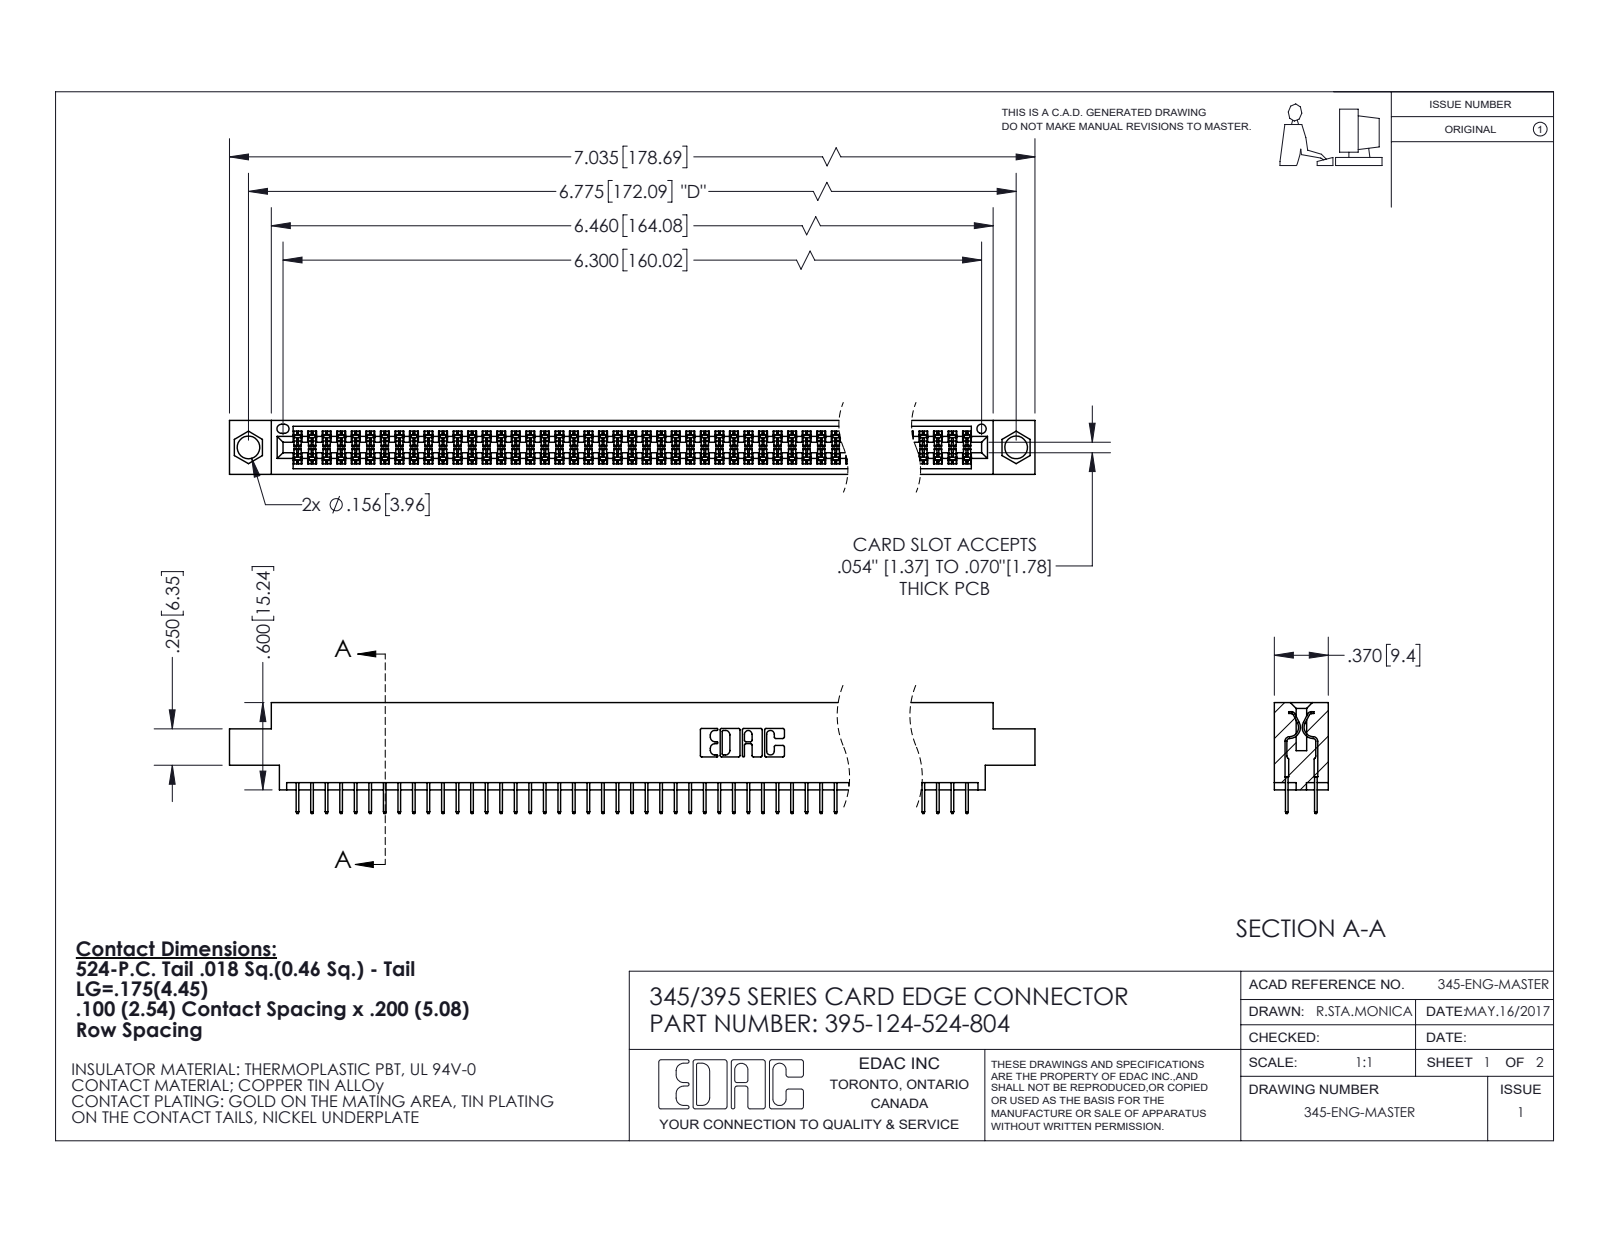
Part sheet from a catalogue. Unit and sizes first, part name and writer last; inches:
Units: inches
Overall size (bounding box): 7.035 × 0.762 × 0.37
Round holes (diameter × count): ⌀0.156 ×2, ⌀0.064 ×1
Partial cylindrical surfaces — rounded edges, fillets, slot ends (radius × count): R0.006 ×247, R0.01 ×22, R0.007 ×6, R0.031 ×6, R0.026 ×3, R0.014 ×2, R0.019 ×2, R0.022 ×2
Main face-to-face distances: 0.072, 0.298, 0.37, 0.2, 0.098, 0.272, 0.025, 0.225, 0.072, 0.175
Hole centre spacings: 0.27, 6.539, 6.775
Volume: 1.046 in³ · Surface area: 39.09 in²
Bodies: 125 solids, 6840 faces (4934 planar, 1906 cylindrical, 0 other)
Part name (STEP PRODUCT): 345-292-001_345-293-124; 345 Part_0.170 Offset - 0.156 Dia-TI; 395-124-524-804
STEP written by: SolidWorks 2020 (CONFIG_CONTROL_DESIGN)
